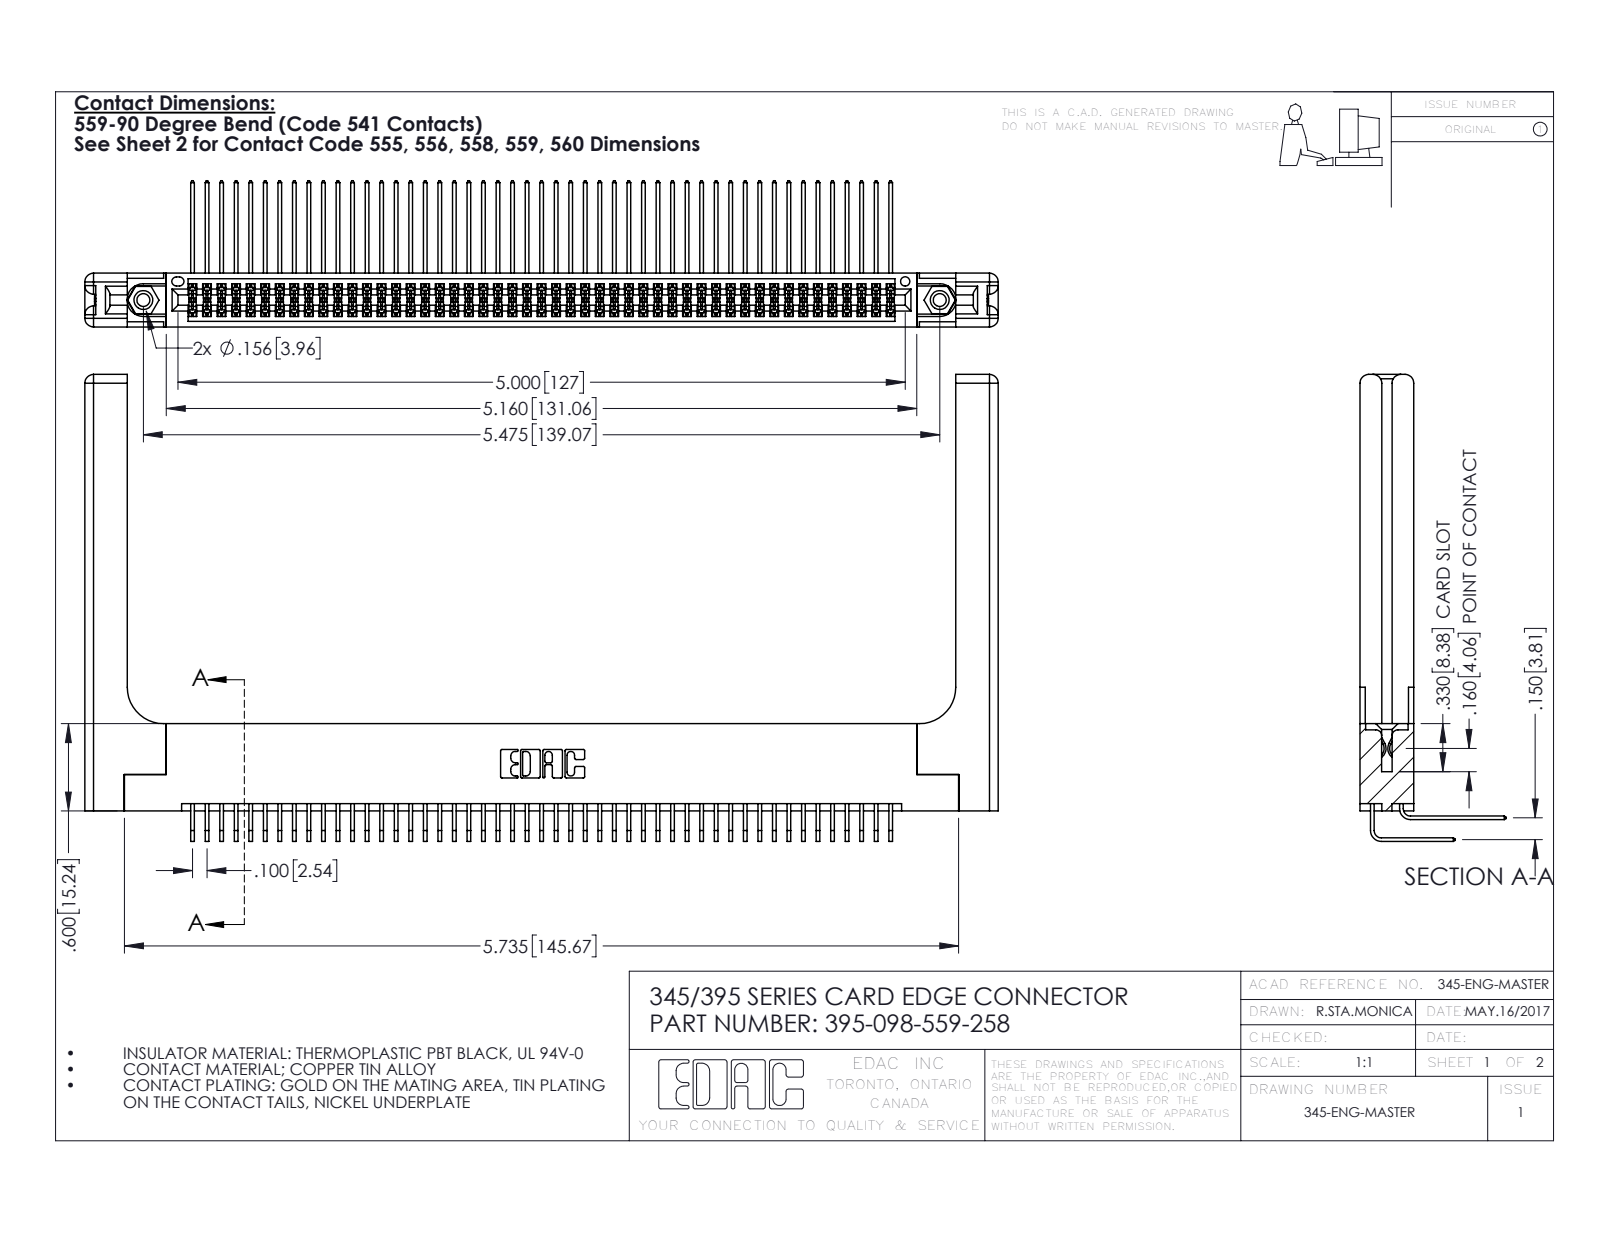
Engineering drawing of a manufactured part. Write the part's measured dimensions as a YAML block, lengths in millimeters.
part_name: "345-250-001_345-250-001-102; 345-292-001_558 559 Tail - 1; 345-220-058_345-220-058; 345-292-001_559 Tail - 2 (+2 more)"
step_written_by: "SolidWorks 2016 (CONFIG_CONTROL_DESIGN)"
units: millimeters
bodies: {solids: 103, faces: 5478, planar: 3658, cylindrical: 1760, other: 60}
overall_size: [159.5, 81.5, 25.5]
volume: 24600
surface_area: 31680
round_holes:
  - {diameter: 2.3, count: 2}
  - {diameter: 3.2, count: 2}
  - {diameter: 4, count: 2}
  - {diameter: 1.6, count: 1}
round_bosses_or_shafts:
  - {diameter: 3.9, count: 2}
partial_cylinders:
  - {radius: 0.2, count: 147}
  - {radius: 0.3, count: 22}
  - {radius: 1.5, count: 16}
  - {radius: 0.2, count: 6}
  - {radius: 0.8, count: 6}
  - {radius: 0.7, count: 3}
  - {radius: 0.4, count: 2}
  - {radius: 0.5, count: 2}
face_to_face_distances: [1.8, 7.6, 9.4, 5.1, 2.5, 6.9, 0.6, 5.7, 4.4, 3.8]
hole_center_spacings: [6.9, 133.1, 139.1]
